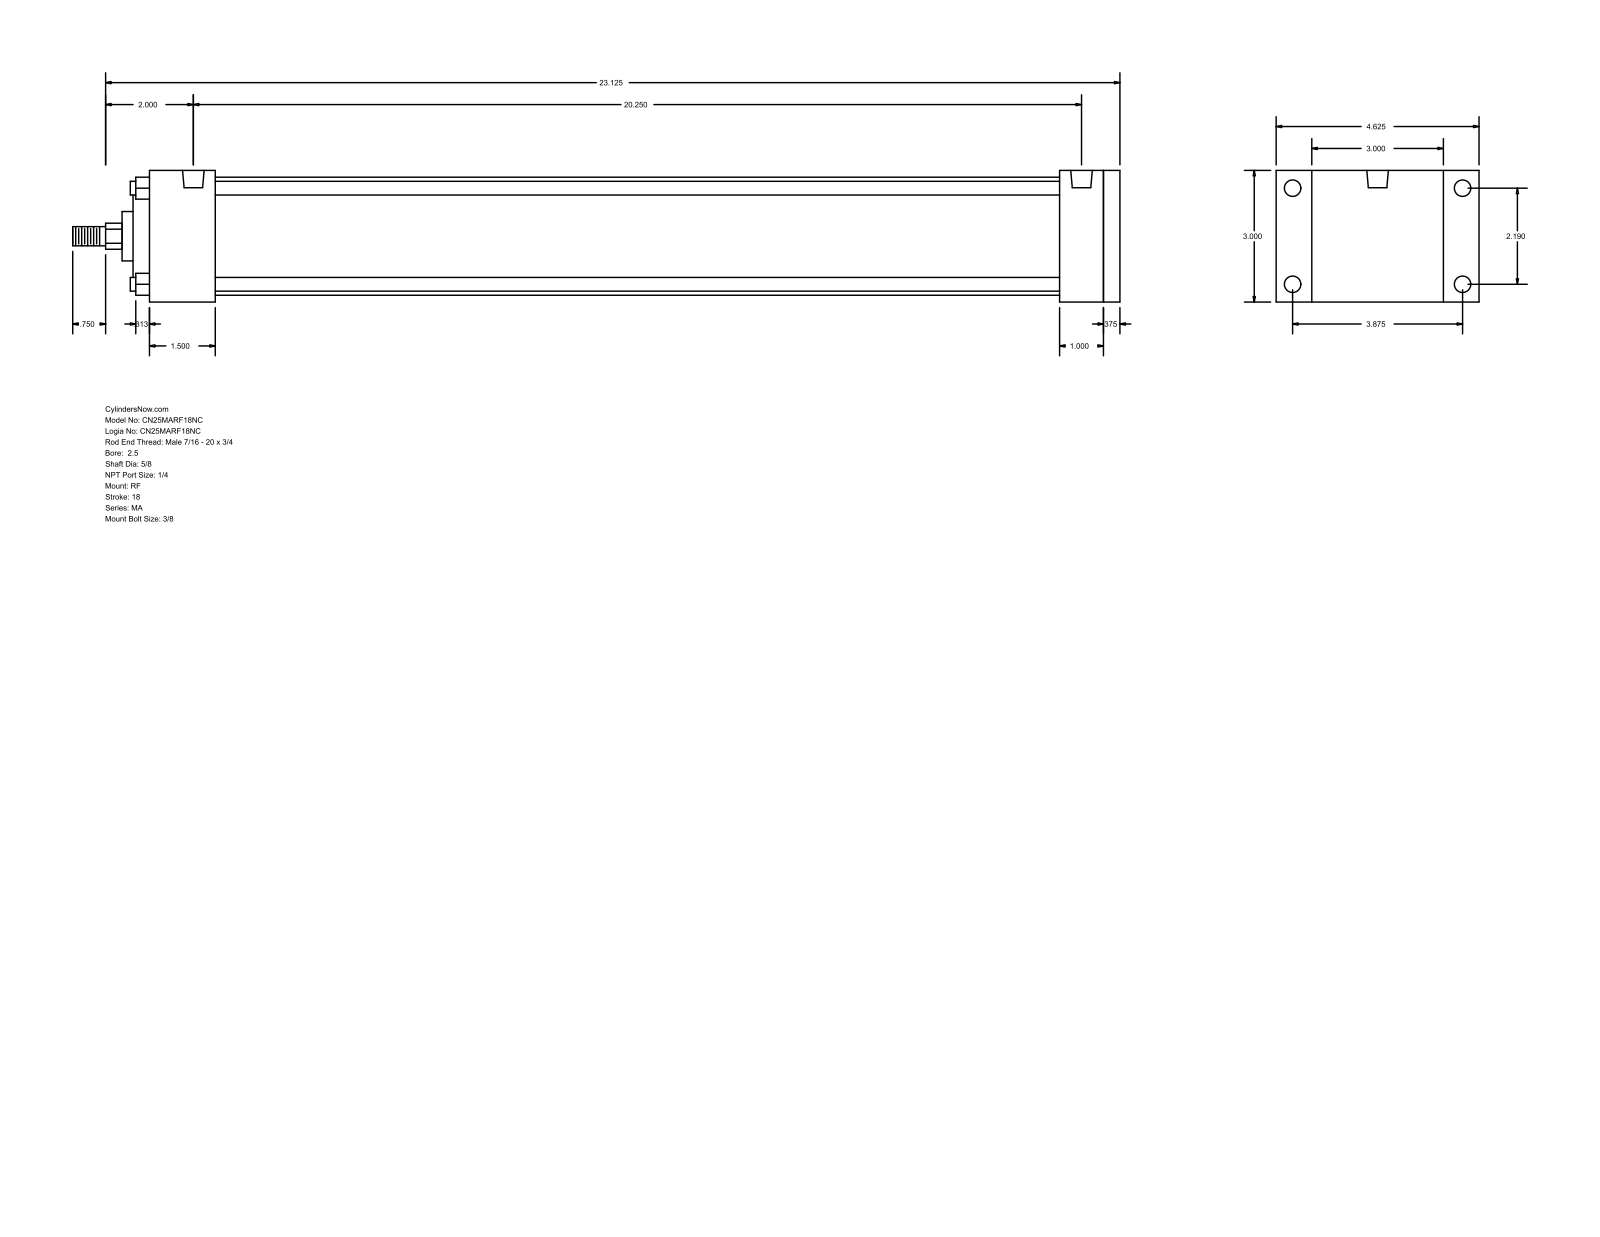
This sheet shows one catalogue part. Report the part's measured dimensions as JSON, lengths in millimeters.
{"part_name": "MA_RF__0250_0.625", "step_written_by": "GSSL Pune (CONFIG_CONTROL_DESIGN)", "units": "millimeters", "bodies": {"solids": 0, "faces": 94, "planar": 65, "cylindrical": 29, "other": 0}, "overall_size": [606.42, 117.47, 76.2], "round_holes": [[7.94, 4], [9.53, 4], [12.49, 2]], "round_bosses_or_shafts": [[7.94, 4], [68.33, 1], [50.8, 1], [28.57, 1], [15.88, 1], [11.11, 1]], "partial_cylinders_radius": [[7.54, 1]], "face_to_face_distances": [76.2, 561.98, 9.53, 552.45, 25.4, 34.93, 38.1, 527.05, 488.95, 514.35], "hole_center_spacings": [55.62, 98.42, 113.05, 514.35]}
